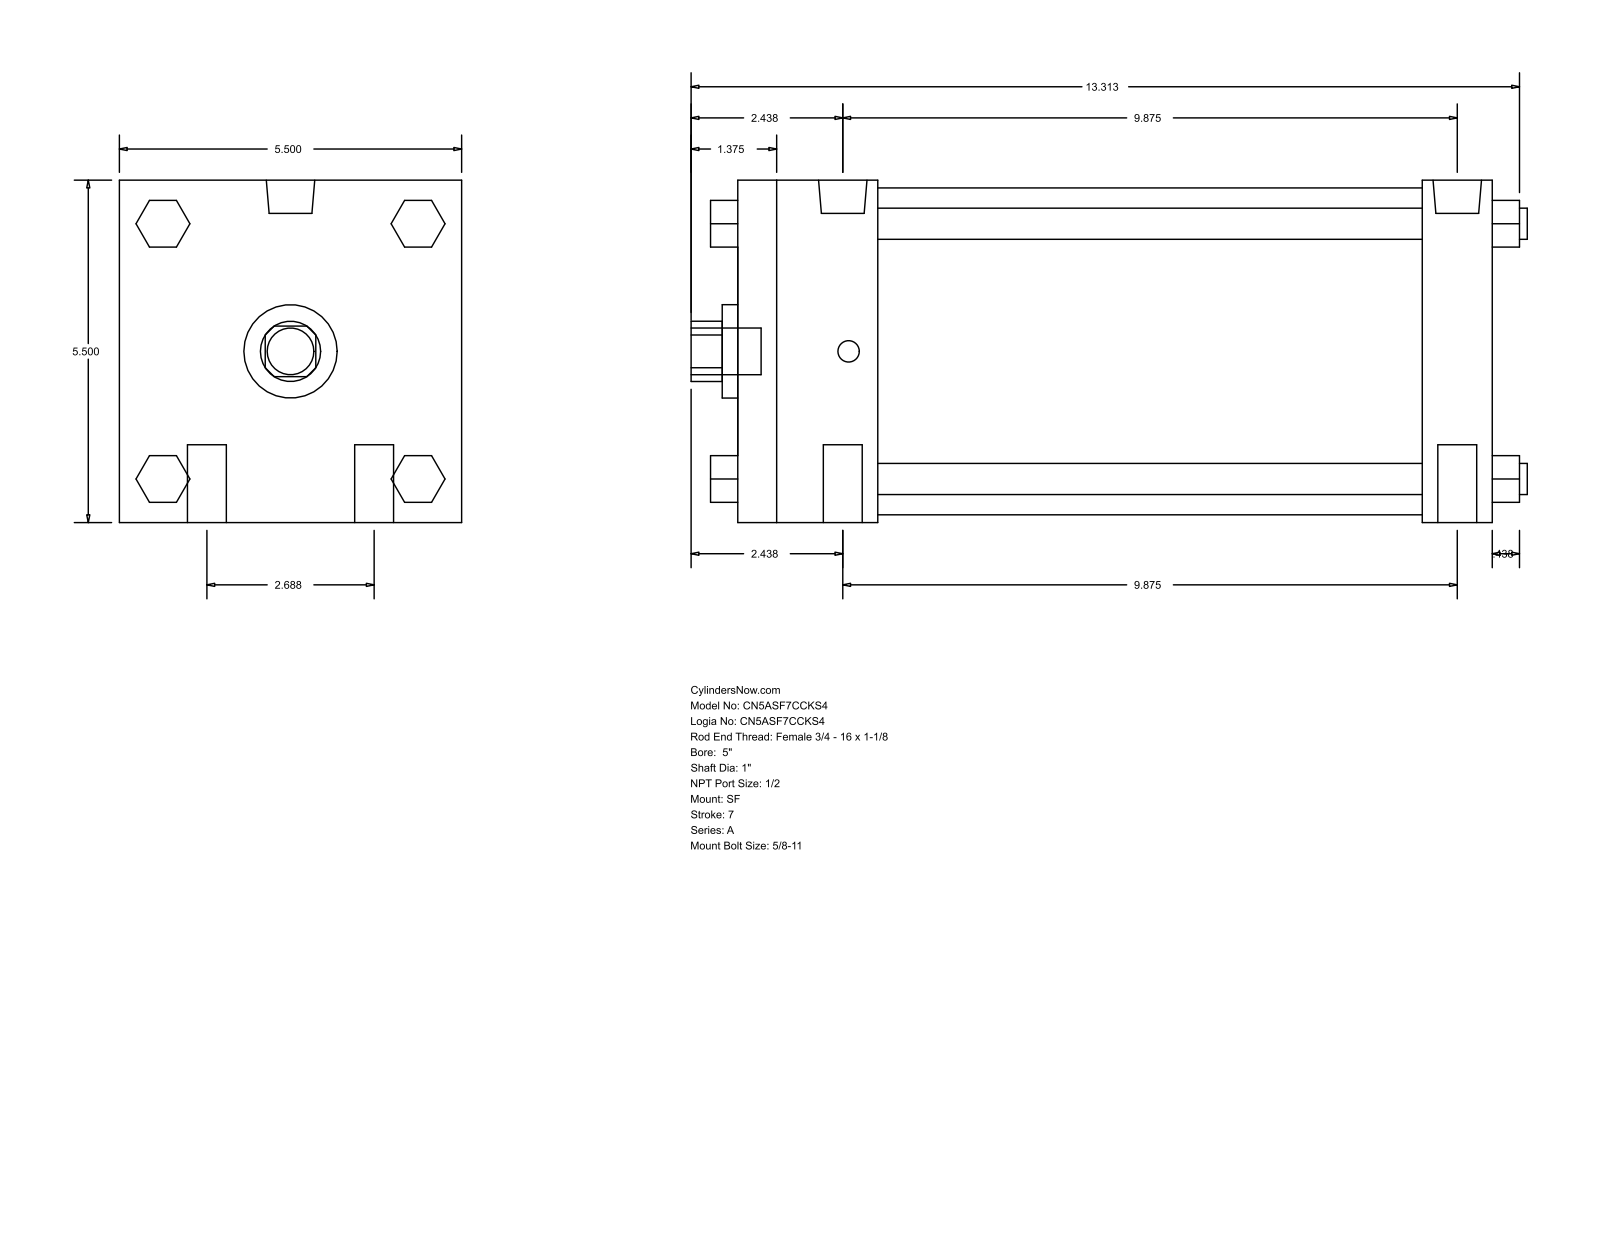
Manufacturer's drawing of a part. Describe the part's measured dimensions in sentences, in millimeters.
The part is named "A_SF__0500_1". Its 3-D file was written by "GSSL Pune (CONFIG_CONTROL_DESIGN)". It is 0 solids with 124 faces: 94 planar, 30 cylindrical and 0 other. Overall it measures 341.31 by 139.7 by 139.7 millimeters. Round holes: 1 of diameter 25.4, 1 of diameter 38.1, 1 of diameter 133.35. Round bosses or shafts: 4 of diameter 15.88, 4 of diameter 12.7, 2 of diameter 19.77, 2 of diameter 8.73, 1 of diameter 19.05. Partial cylindrical surfaces (rounded edges, fillets, slot ends): 1 of radius 12.29. The main face-to-face distances are 139.7, 307.97, 28.57, 57.15, 279.4, 222.25, 250.82, 19.05, 52.07, 90.18.
